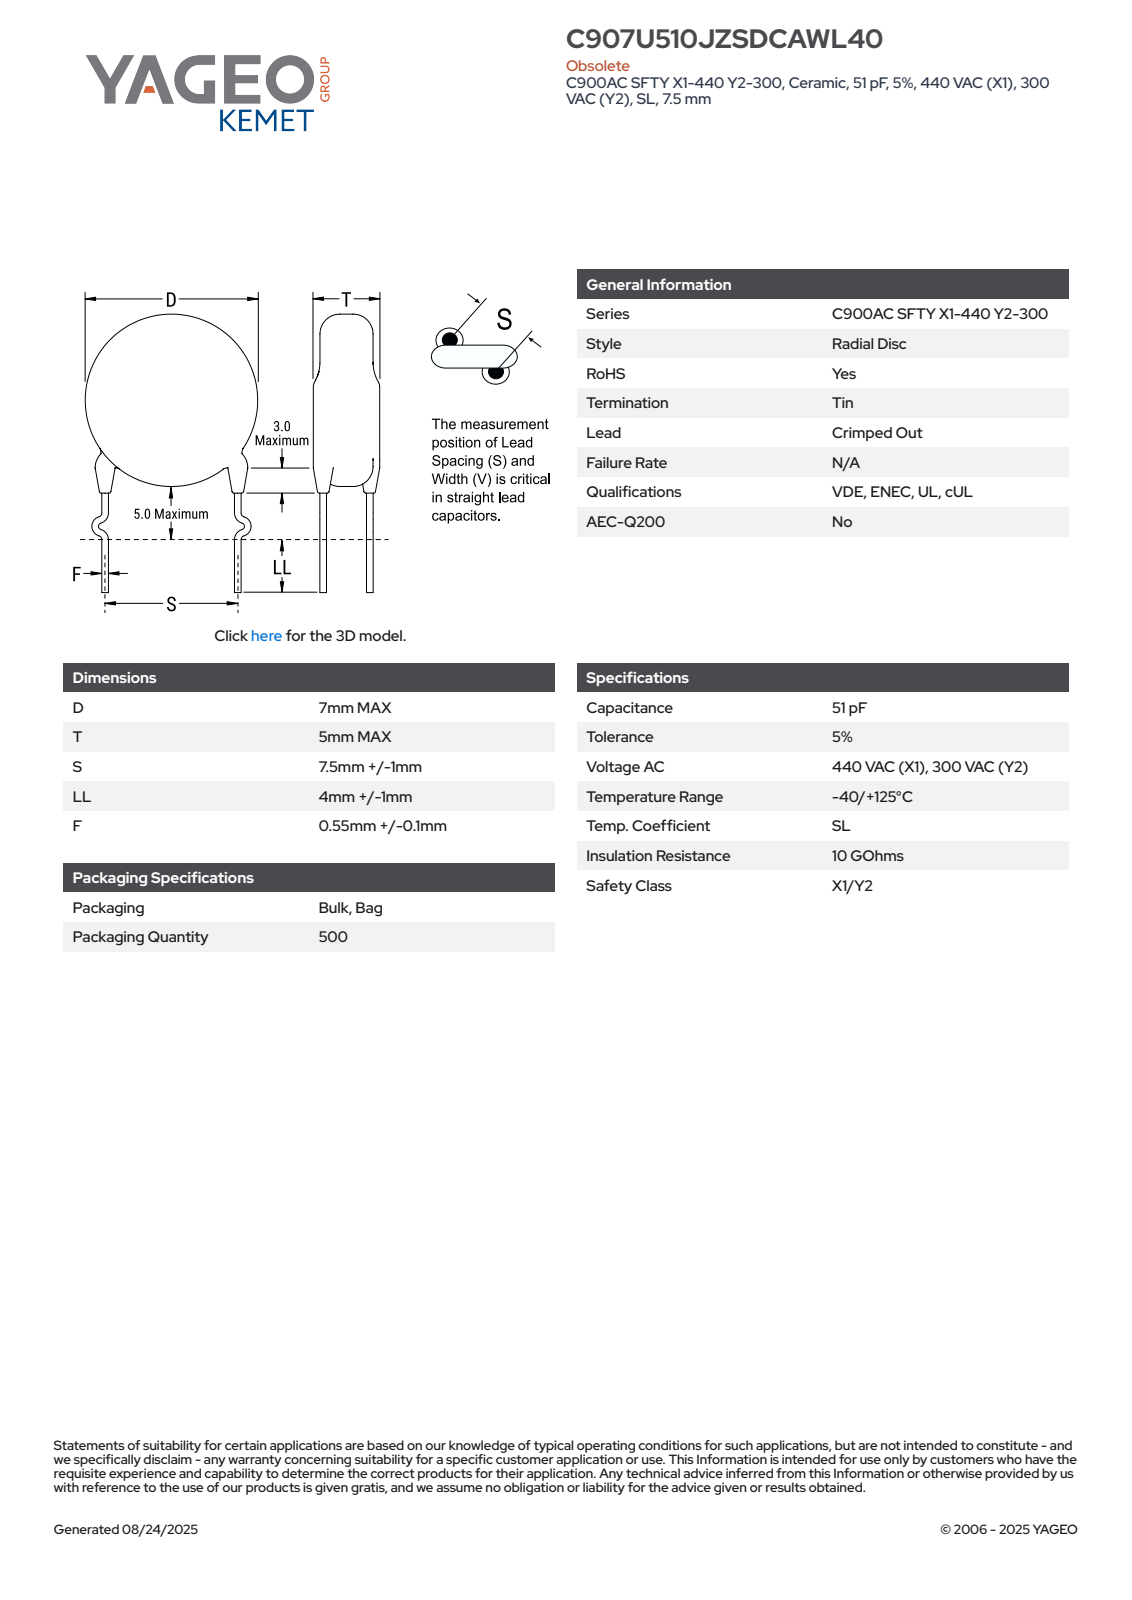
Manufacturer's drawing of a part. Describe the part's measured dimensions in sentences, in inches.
The part is named "CCD_KCOC900_D7T5S7.5LL5F0.55". Its 3-D file was written by "SolidWorks 2014 (AUTOMOTIVE_DESIGN)". It is 4 solids with 87 faces: 63 planar, 6 cylindrical and 18 other. Overall it measures 0.669 by 0.466 by 0.215 inches. Its volume is 0.012 cubic inches and its surface area 0.367 square inches. Round bosses or shafts: 2 of diameter 0.047, 1 of diameter 0.276. The main face-to-face distances are 0.197, 0.029, 0.152, 0.124, 0.023, 0.013, 0.117, 0.059, 0.085, 0.088.
